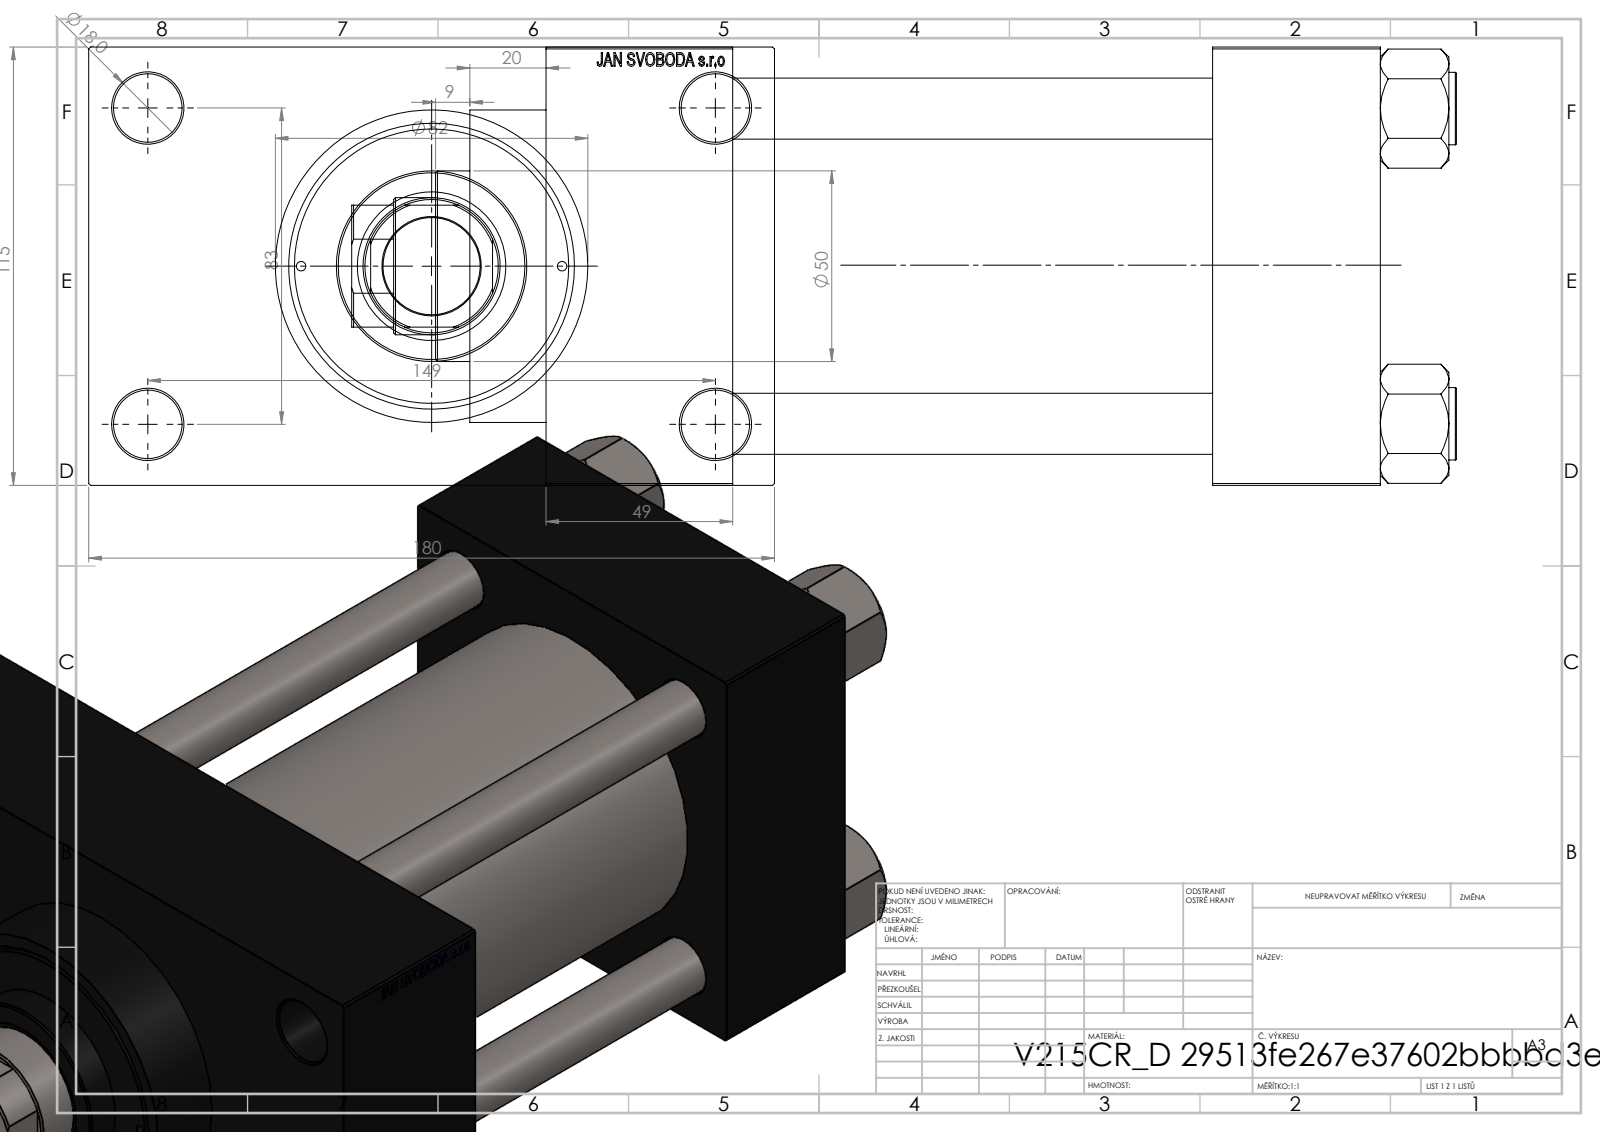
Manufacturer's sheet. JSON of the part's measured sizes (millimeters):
{"part_name": "V215CR_D_Body; V215CR_VCP_D; V215CR_D_TYCINKA; V215_VC_A (+1 more)", "step_written_by": "SolidWorks 2019 (CONFIG_CONTROL_DESIGN)", "units": "millimeters", "bodies": {"solids": 11, "faces": 1159, "planar": 547, "cylindrical": 92, "other": 520}, "overall_size": [290, 180, 115], "volume_mm3": 2135000, "surface_area_mm2": 346617, "round_holes": [[16, 4], [18, 4], [2.5, 2], [7, 2], [26.44, 2], [35, 2], [25.5, 1], [36, 1], [39, 1], [61, 1], [72, 1], [80, 1]], "round_bosses_or_shafts": [[19, 4], [86, 1], [82, 1], [50, 1]], "partial_cylinders_radius": [[17.5, 1]], "face_to_face_distances": [115, 126, 175, 49, 170, 44, 219, 32.5, 147.5, 180], "hole_center_spacings": [33.15, 41.96, 57.81, 58.48, 82.7, 85.28, 86.17, 89.24]}
